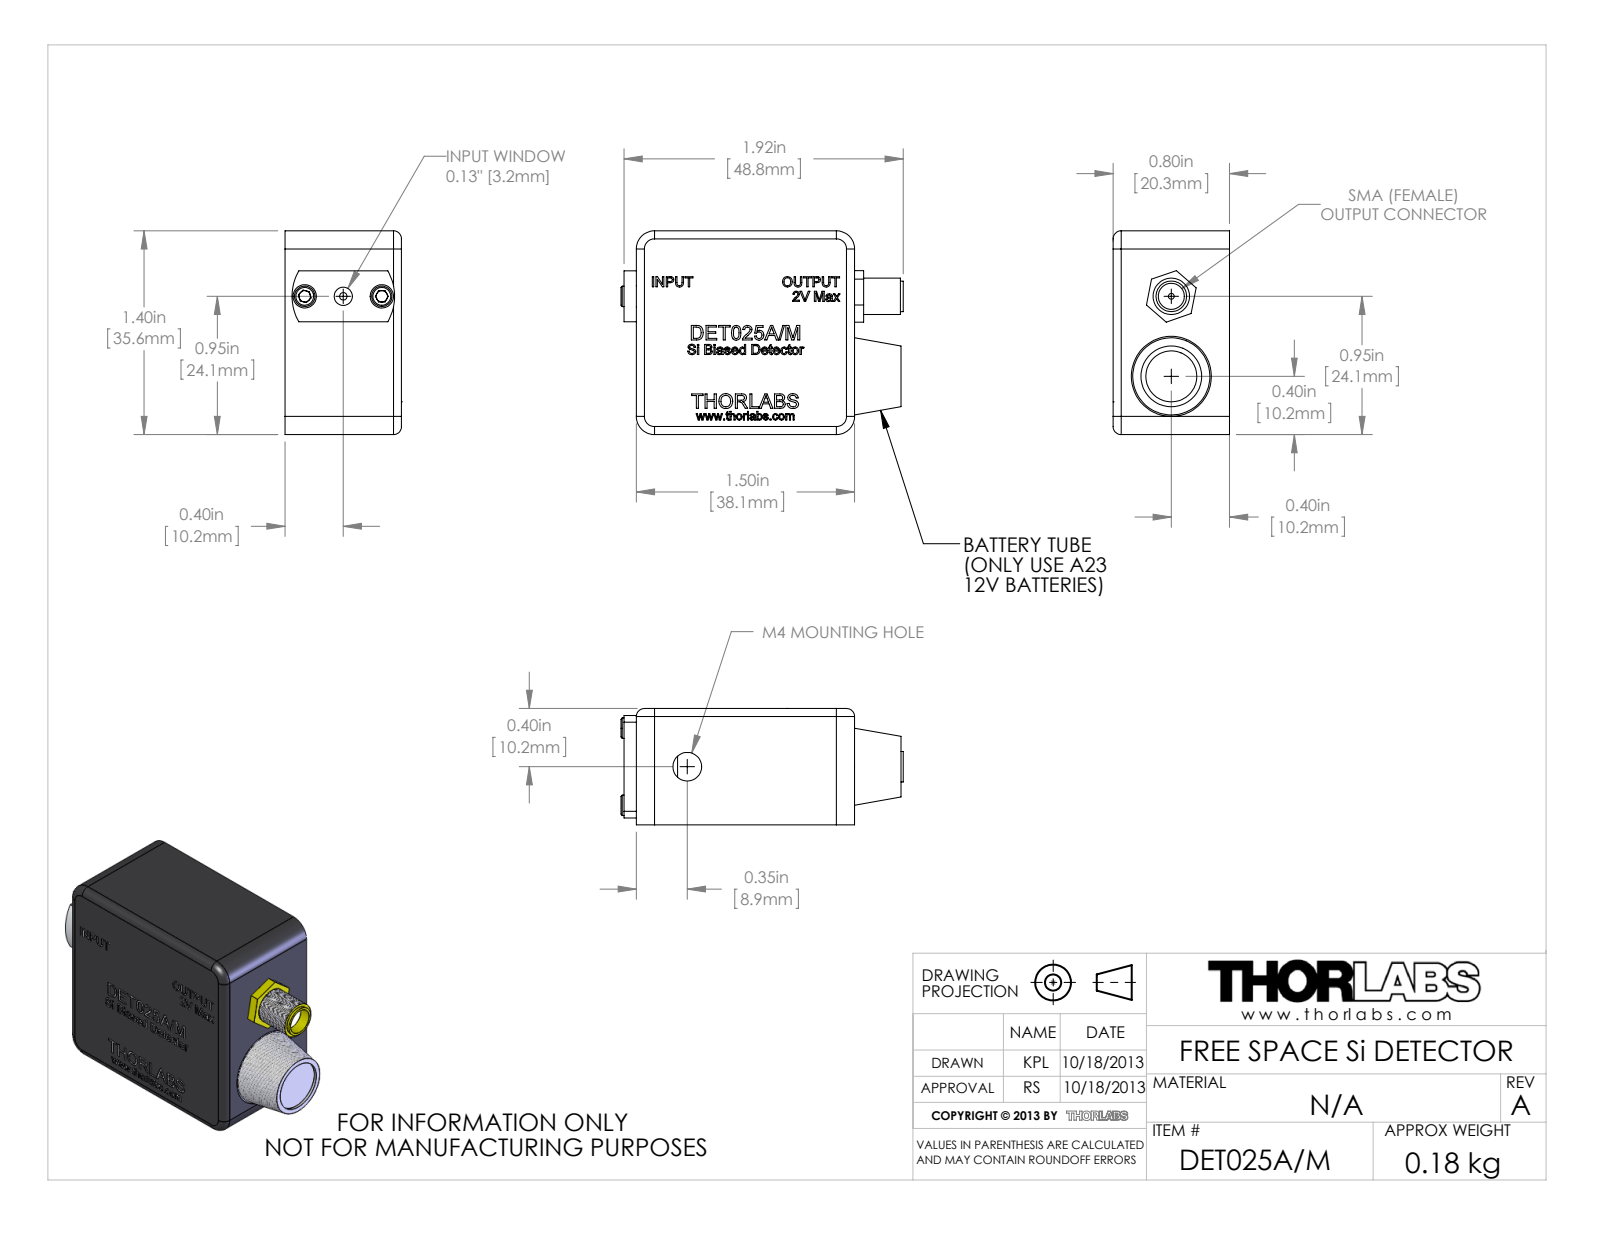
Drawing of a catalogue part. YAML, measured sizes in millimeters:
part_name: "TTN020153; flat head screw_ai_CR-FHMS 0.086-56x0.188x0.188-N; socket head cap screw_ai_HX-SHCS 0.086-56x0.188x0.188-N; TTN020132 (+5 more)"
step_written_by: "SolidWorks 2012 (AUTOMOTIVE_DESIGN)"
units: millimeters
bodies: {solids: 12, faces: 1632, planar: 984, cylindrical: 167, other: 481}
overall_size: [49.3, 35.6, 20.3]
volume: 17260
surface_area: 13630
round_holes:
  - {diameter: 1.8, count: 6}
  - {diameter: 2.4, count: 4}
  - {diameter: 3.2, count: 4}
  - {diameter: 3.6, count: 4}
  - {diameter: 2.2, count: 2}
  - {diameter: 4.1, count: 2}
  - {diameter: 0.4, count: 1}
  - {diameter: 1, count: 1}
  - {diameter: 1.3, count: 1}
  - {diameter: 3.2, count: 1}
  - {diameter: 4.5, count: 1}
  - {diameter: 4.7, count: 1}
round_bosses_or_shafts:
  - {diameter: 2.2, count: 6}
  - {diameter: 3.7, count: 4}
  - {diameter: 3.6, count: 2}
  - {diameter: 12, count: 1}
  - {diameter: 11, count: 1}
  - {diameter: 8.3, count: 1}
  - {diameter: 7.9, count: 1}
  - {diameter: 5.8, count: 1}
partial_cylinders:
  - {radius: 3.2, count: 12}
  - {radius: 0.8, count: 4}
  - {radius: 1.4, count: 4}
  - {radius: 2, count: 4}
  - {radius: 2.4, count: 4}
  - {radius: 1.5, count: 2}
  - {radius: 2.5, count: 2}
  - {radius: 0.2, count: 1}
face_to_face_distances: [1.6, 18.7, 20.3, 35.6, 12.7, 14.3, 6, 2.5, 38.1, 33]
hole_center_spacings: [43.1, 29.2, 29.2, 31.8, 31.8, 6.7, 15.5, 33.8]
